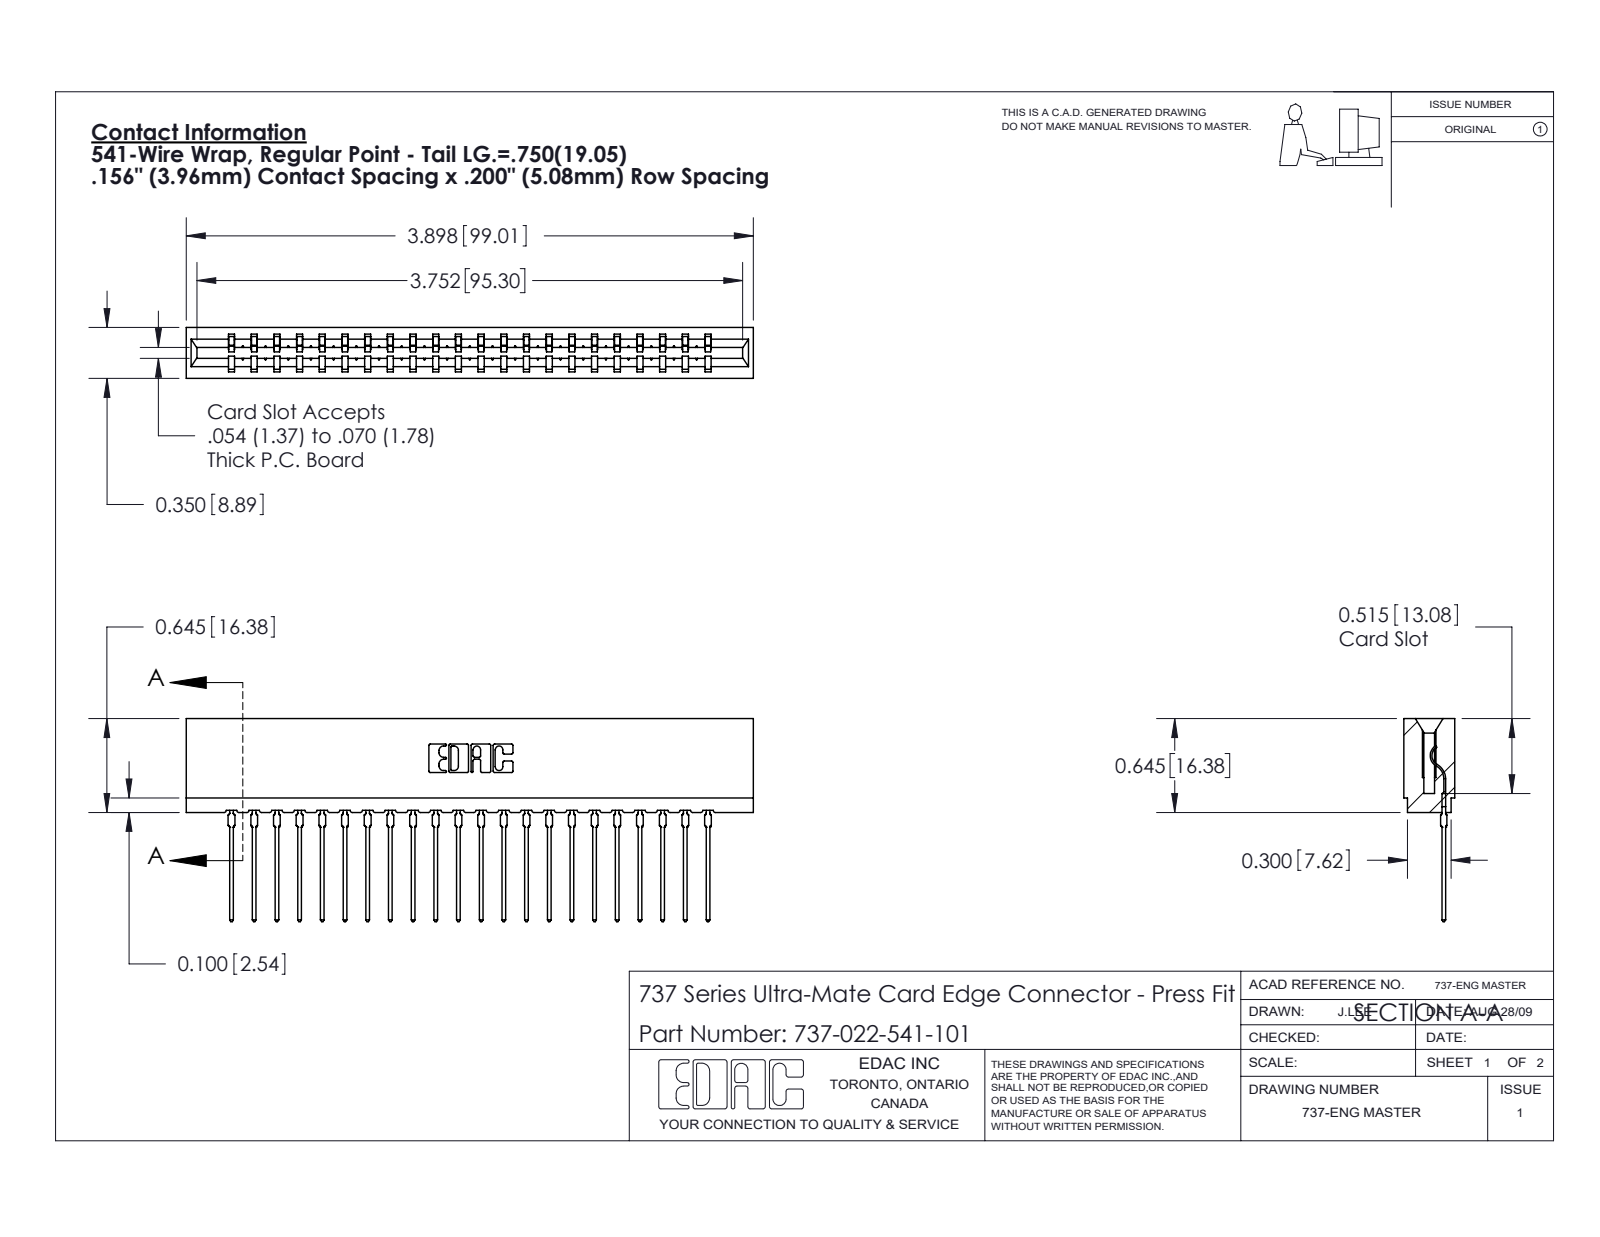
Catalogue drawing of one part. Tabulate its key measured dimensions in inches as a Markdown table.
| quantity | value |
| --- | --- |
| part name | 745-292-001_541; 737 Part_Insulator Option - 01; 737-022-541-101 |
| STEP written by | SolidWorks 2020 (CONFIG_CONTROL_DESIGN) |
| units | inches |
| bodies | 23 solids, 2580 faces (1550 planar, 458 cylindrical, 572 other) |
| overall size | 3.898 × 1.396 × 0.35 |
| volume | 0.598 in³ |
| surface area | 20.58 in² |
| partial cylindrical surfaces (radius × count) | 0.015 × 44, 0.021 × 44, 0.01 × 22, 0.007 × 6, 0.031 × 6, 0.005 × 4, 0.011 × 4, 0.026 × 3 |
| main face-to-face distances | 0.138, 0.212, 0.35, 0.156, 0.074, 0.624, 0.063, 0.287, 0.076, 0.149 |
